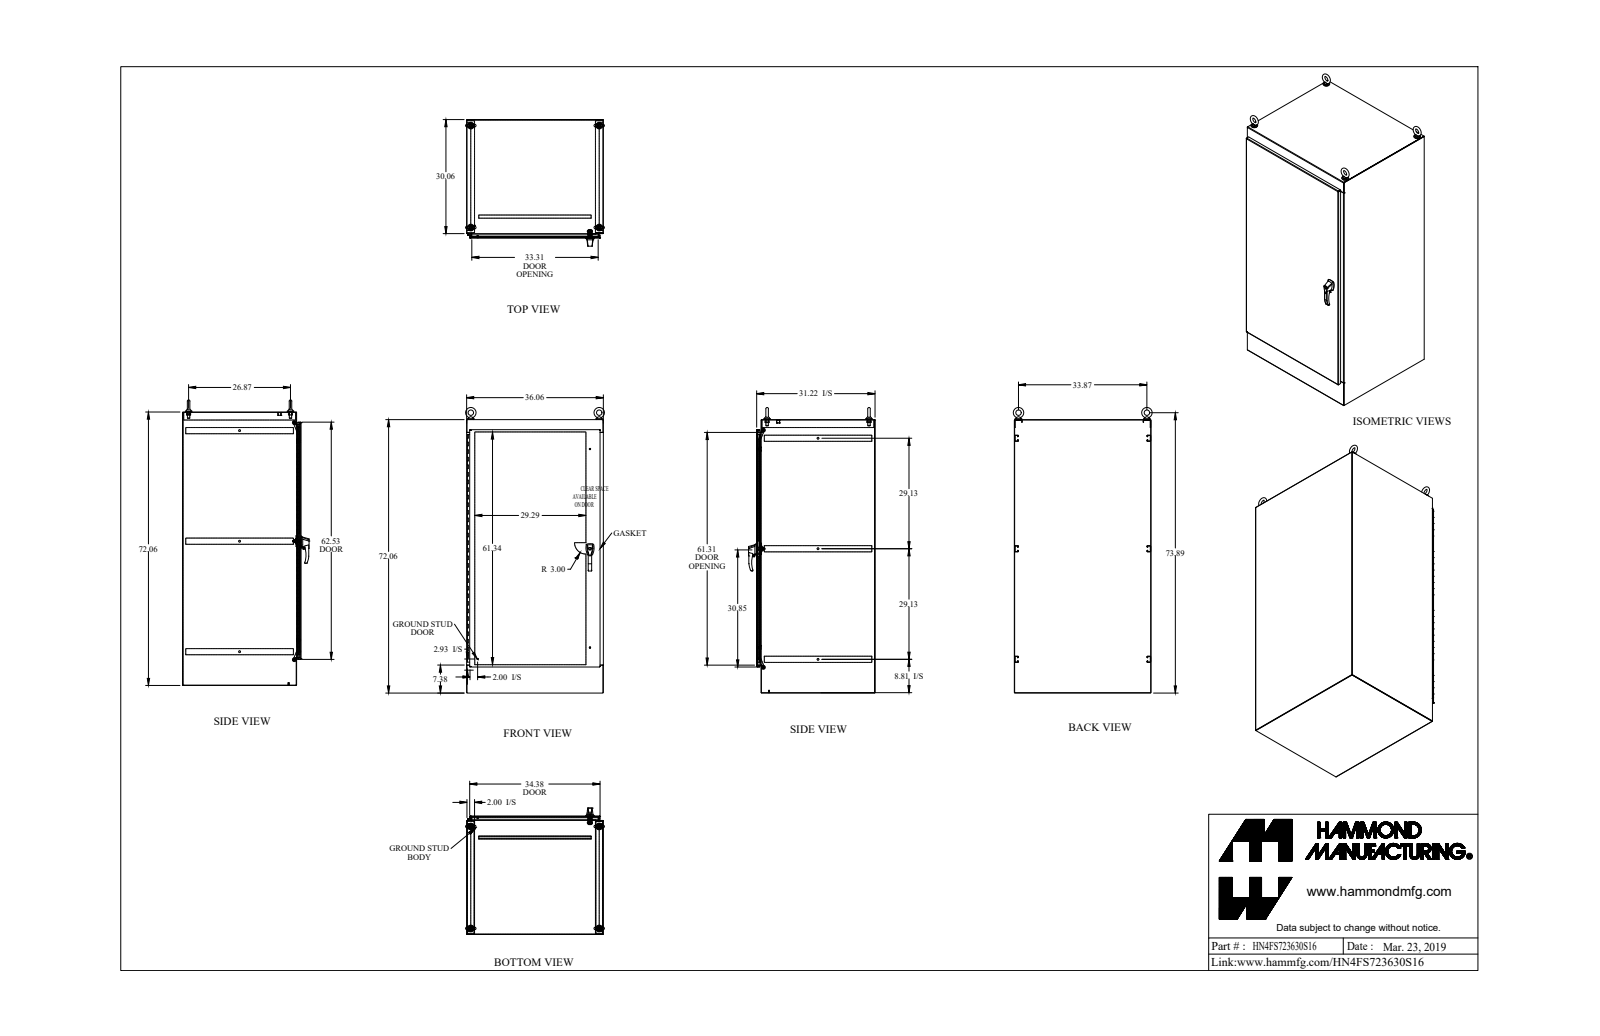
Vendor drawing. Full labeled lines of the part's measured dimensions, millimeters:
Part name (STEP PRODUCT): HN4FS723630S16
STEP written by: SolidWorks 2018 (AUTOMOTIVE_DESIGN)
Units: millimetres
Bodies: 65 solids, 2016 faces (905 planar, 886 cylindrical, 225 other)
Overall size (bounding box): 1917.4 × 929.7 × 847.4
Volume: 21 830 000 mm³ · Surface area: 17 990 000 mm²
Round holes (diameter × count): ⌀7.7 ×10, ⌀8.9 ×7, ⌀19.1 ×6, ⌀13.4 ×4, ⌀15.9 ×4, ⌀17.3 ×4, ⌀12.7 ×3, ⌀6.4 ×2, ⌀6.5 ×2, ⌀7.1 ×2, ⌀7.1 ×2, ⌀8 ×2
Round bosses / shafts (diameter × count): ⌀44.5 ×4, ⌀38.1 ×4, ⌀31.8 ×4, ⌀18.7 ×4, ⌀25.4 ×2, ⌀19.1 ×2, ⌀16 ×2, ⌀15.9 ×2
Partial cylindrical surfaces — rounded edges, fillets, slot ends (radius × count): R1.1 ×42, R3.5 ×36, R12.7 ×23, R3.2 ×22, R0.5 ×16, R1.5 ×15, R1.2 ×13, R3.6 ×13
Main face-to-face distances: 2.4, 791.3, 913.5, 911.1, 788.8, 915.9, 1827.9, 793.7, 1825.5, 1830.3
Hole centre spacings: 152.4, 304.8, 457.2, 609.6, 762, 860.3, 914.4, 1066.8
